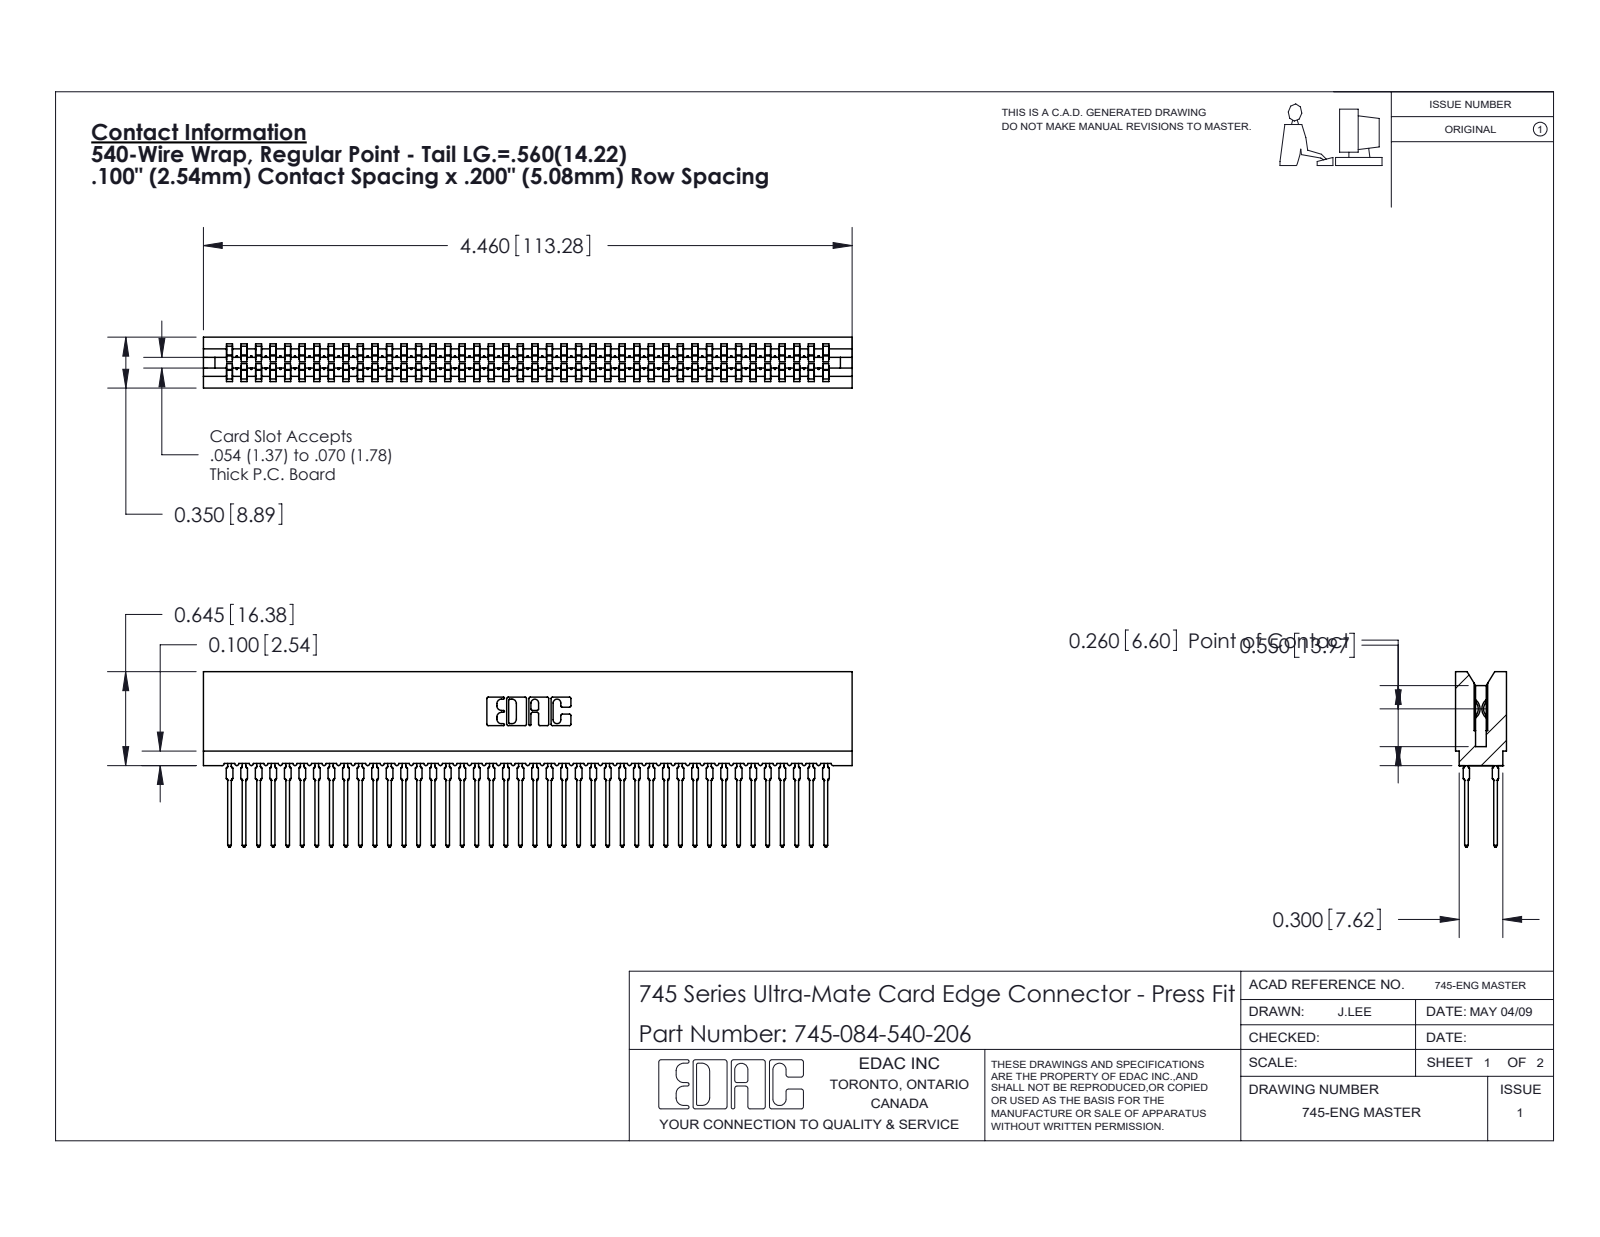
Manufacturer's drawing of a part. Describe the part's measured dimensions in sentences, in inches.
The part is named "745-292-001_540; 745 Part_Insulator Option - 06; 745-084-540-206". Its 3-D file was written by "SolidWorks 2020 (CONFIG_CONTROL_DESIGN)". It is 85 solids with 7614 faces: 3920 planar, 1510 cylindrical and 2184 other. Overall it measures 4.46 by 1.206 by 0.35 inches. Its volume is 0.636 cubic inches and its surface area 34.4 square inches. Partial cylindrical surfaces (rounded edges, fillets, slot ends): 168 of radius 0.021, 84 of radius 0.015, 22 of radius 0.01, 8 of radius 0.005, 8 of radius 0.011, 6 of radius 0.007, 6 of radius 0.031, 3 of radius 0.026. The main face-to-face distances are 0.063, 0.287, 0.35, 0.2, 0.138, 0.212, 0.076, 0.149, 0.045, 0.305.
